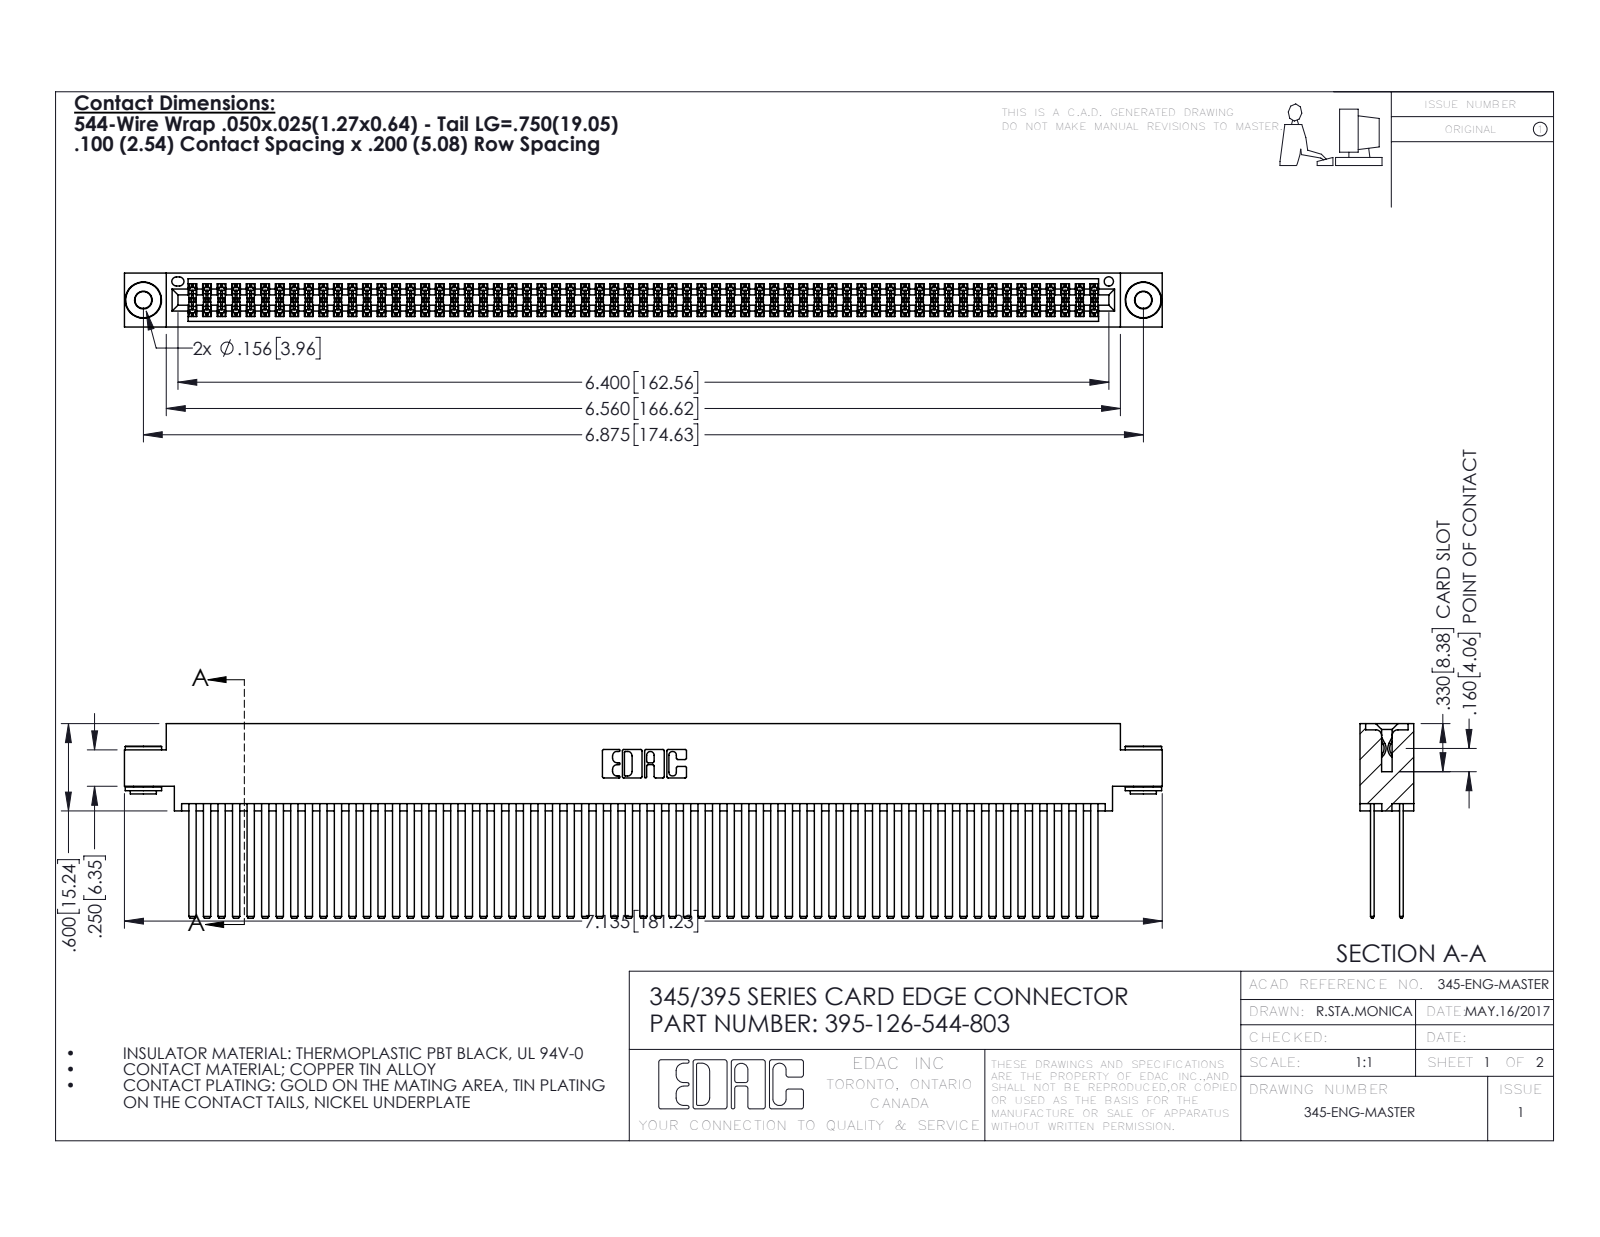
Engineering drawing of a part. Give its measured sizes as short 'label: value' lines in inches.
name: 395-126-544-803; 345 Part_0.170 Offset - 0.156 Dia-TH; 345-250-002_345-250-002-102; 345-292-001_345-293-144
written by: SolidWorks 2016 (CONFIG_CONTROL_DESIGN)
unit: in
bodies: 129 solids, 5712 faces (3748 planar, 1956 cylindrical, 8 other)
size: 7.135 × 1.337 × 0.37
volume: 1.188 in³; area: 53.81 in²
holes: 2× ⌀0.116, 2× ⌀0.156, 1× ⌀0.064
bosses: 2× ⌀0.25, 2× ⌀0.18, 2× ⌀0.136
rounds: 189× R0.006, 22× R0.01, 6× R0.007, 6× R0.031, 3× R0.026, 2× R0.014, 2× R0.019, 2× R0.022
face distances: 0.2, 0.025, 0.072, 0.098, 0.272, 0.298, 0.225, 0.175, 0.37, 0.15
hole spacings: 0.27, 6.639, 6.875
